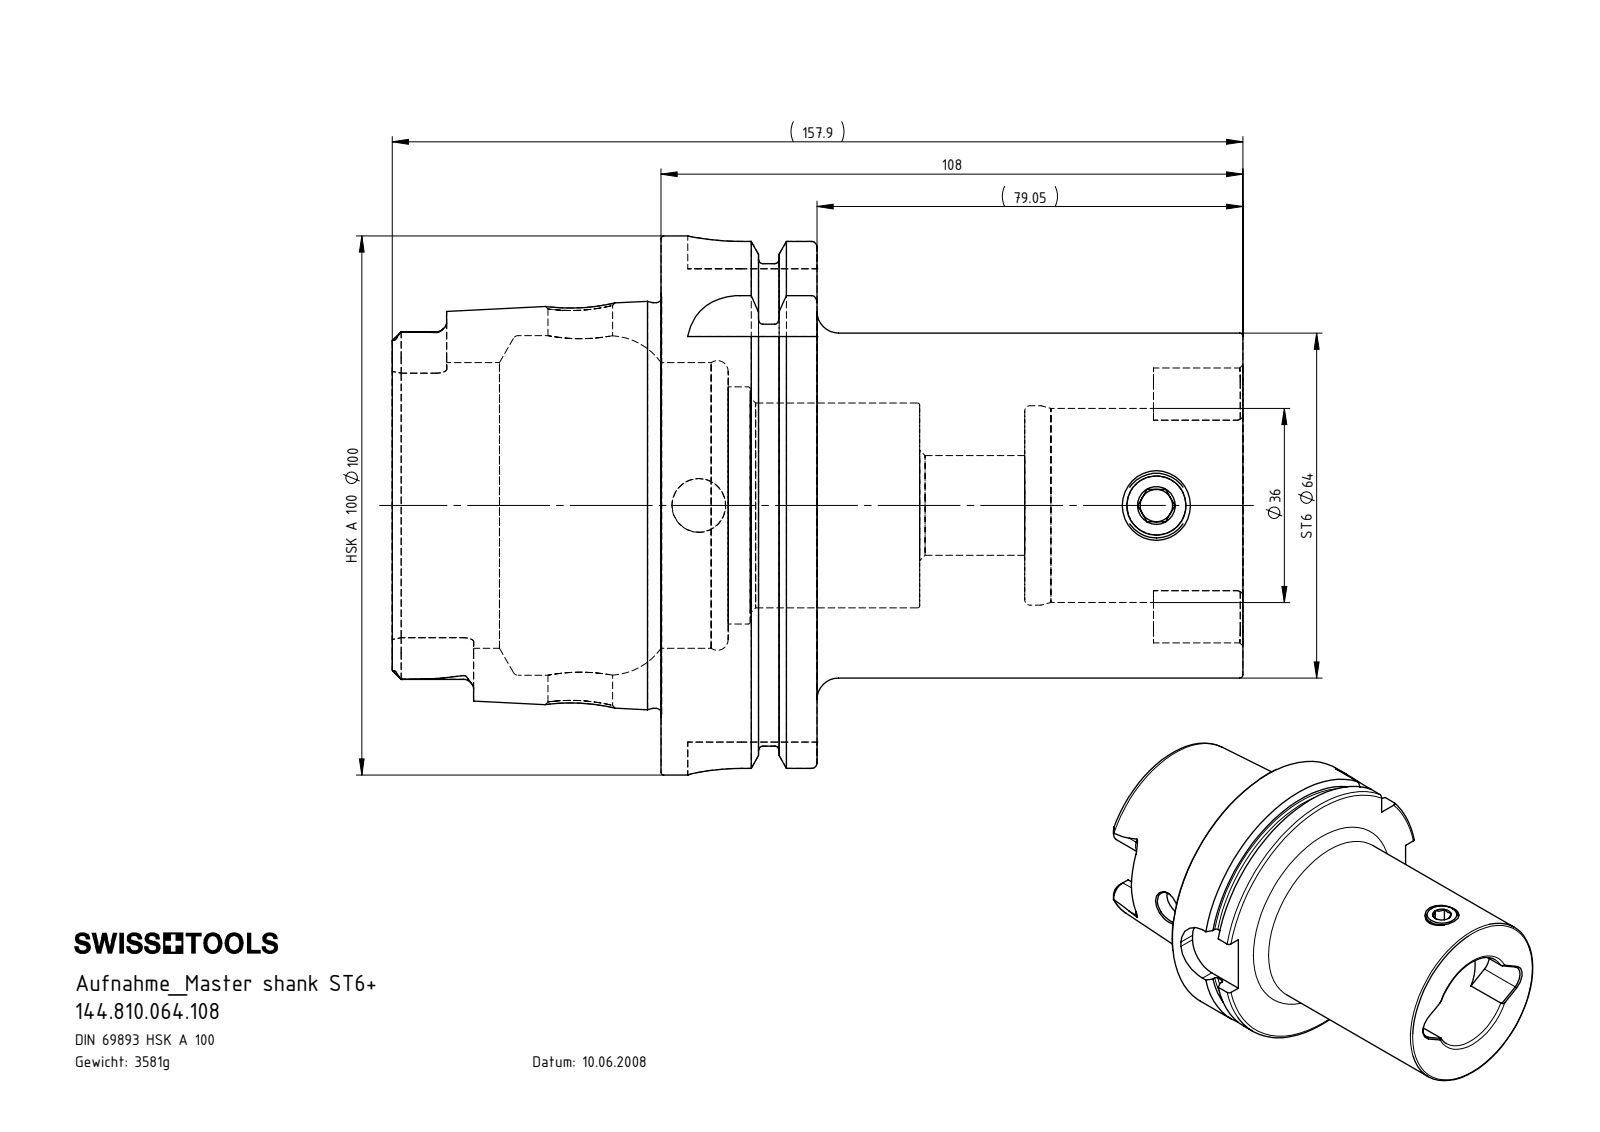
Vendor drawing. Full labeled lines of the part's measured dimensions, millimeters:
Part name (STEP PRODUCT): HA0-ST6.K01.108; ST7-ER4.002.020_A; HA0-ST6.K01.108_A_Fertigbearbeitung; ST6-ER1.001.018_A (+1 more)
STEP written by: SolidWorks 2017 (AUTOMOTIVE_DESIGN)
Units: millimetres
Bodies: 4 solids, 293 faces (83 planar, 92 cylindrical, 118 other)
Overall size (bounding box): 157.9 × 100 × 100
Volume: 456 135 mm³ · Surface area: 87 322 mm²
Round holes (diameter × count): ⌀12 ×2, ⌀6 ×1, ⌀8.5 ×1, ⌀10 ×1, ⌀11 ×1, ⌀18.5 ×1, ⌀22.5 ×1, ⌀24.6 ×1, ⌀36 ×1, ⌀37 ×1, ⌀38 ×1, ⌀44 ×1
Round bosses / shafts (diameter × count): ⌀100 ×1, ⌀91.95 ×1, ⌀75.26 ×1, ⌀64 ×1, ⌀43.5 ×1, ⌀40 ×1, ⌀27 ×1, ⌀18 ×1
Partial cylindrical surfaces — rounded edges, fillets, slot ends (radius × count): R1.6 ×6, R1.9 ×6, R4.5 ×6, R4.88 ×4, R10 ×4, R5.2 ×2
Main face-to-face distances: 28.95, 108, 79.05, 20, 75.45, 12.55, 62.45, 78.85, 48, 19.05
Hole centre spacings: 84.95
